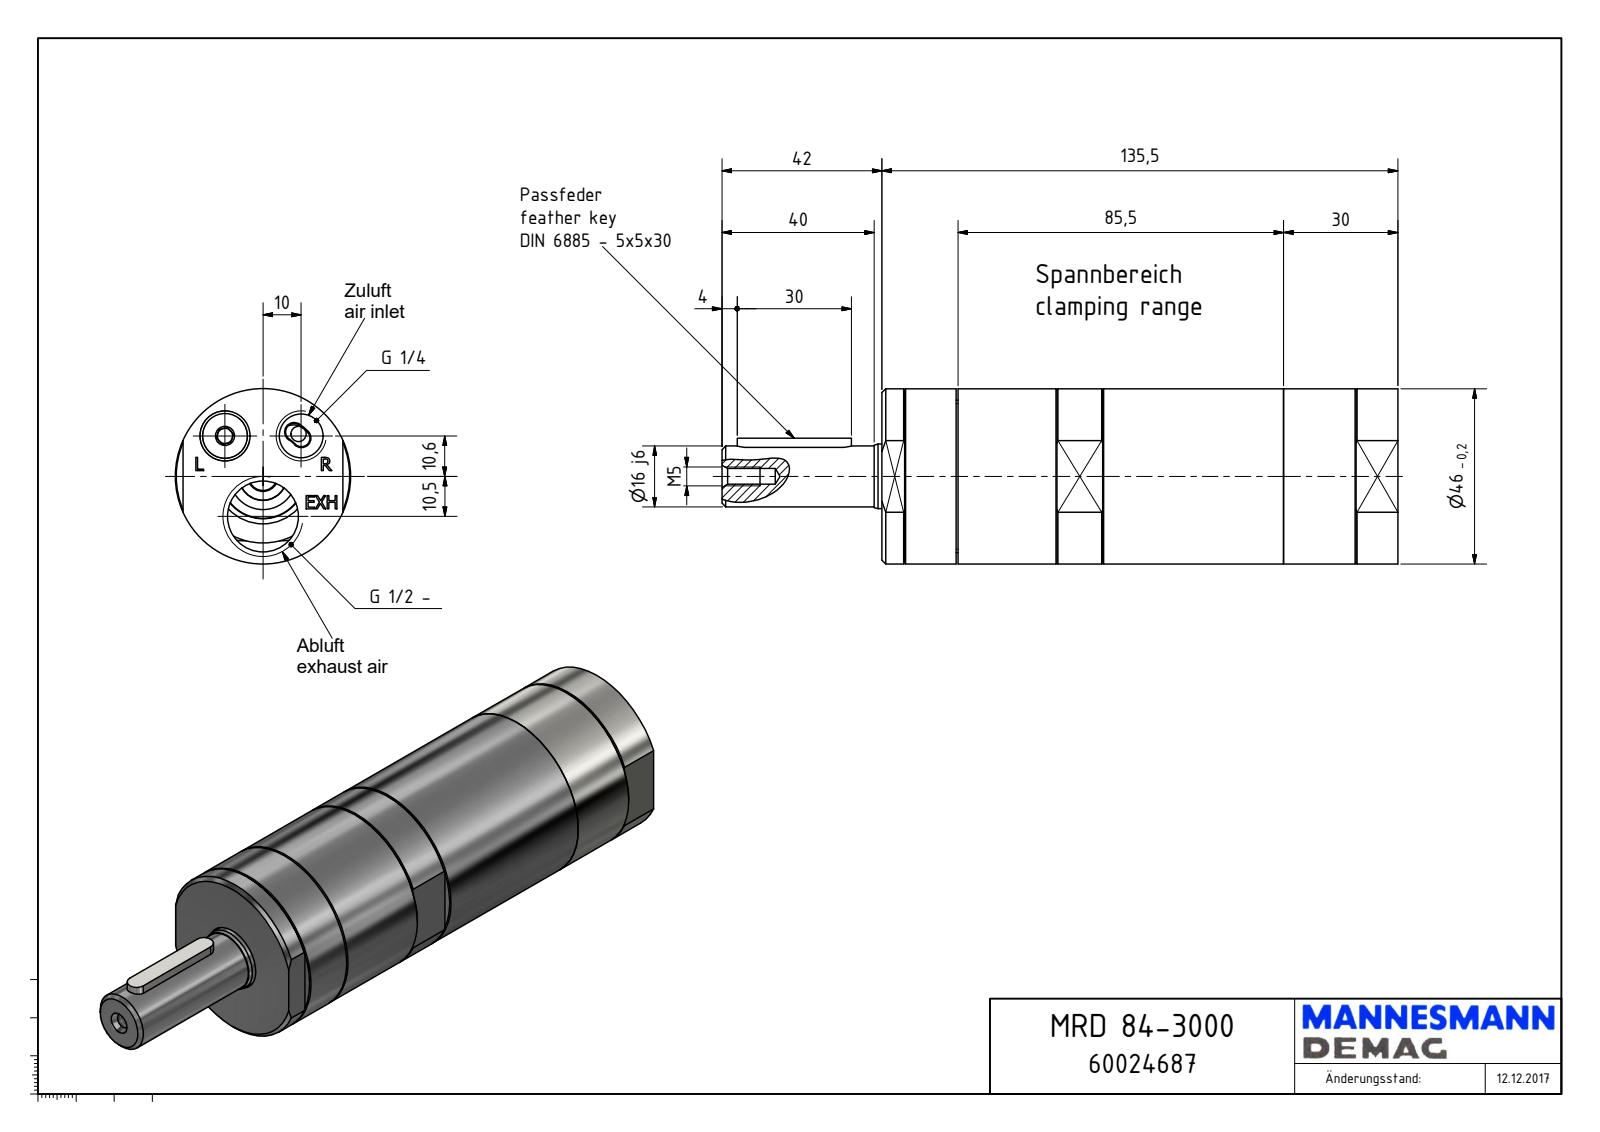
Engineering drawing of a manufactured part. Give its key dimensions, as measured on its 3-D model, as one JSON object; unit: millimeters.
{"part_name": "MRD 84-3000_60024687", "step_written_by": "Autodesk Inventor 2018 (AUTOMOTIVE_DESIGN)", "units": "millimeters", "bodies": {"solids": 1, "faces": 164, "planar": 105, "cylindrical": 28, "other": 31}, "overall_size": [177.5, 46, 46], "volume_mm3": 228182, "surface_area_mm2": 28100, "round_holes": [[4, 1], [4.13, 1], [11.45, 1], [17.5, 1], [18.63, 1]], "round_bosses_or_shafts": [[46, 1], [40, 1], [33.33, 1], [16.95, 1], [16, 1]], "partial_cylinders_radius": [[2.5, 2], [5, 2], [5.72, 1], [19, 1]], "face_to_face_distances": [135.5, 42, 19.5, 20, 0.5, 116, 115.5, 7.46, 128.04, 108.54], "hole_center_spacings": [14.57, 23.35, 10.5, 20]}
